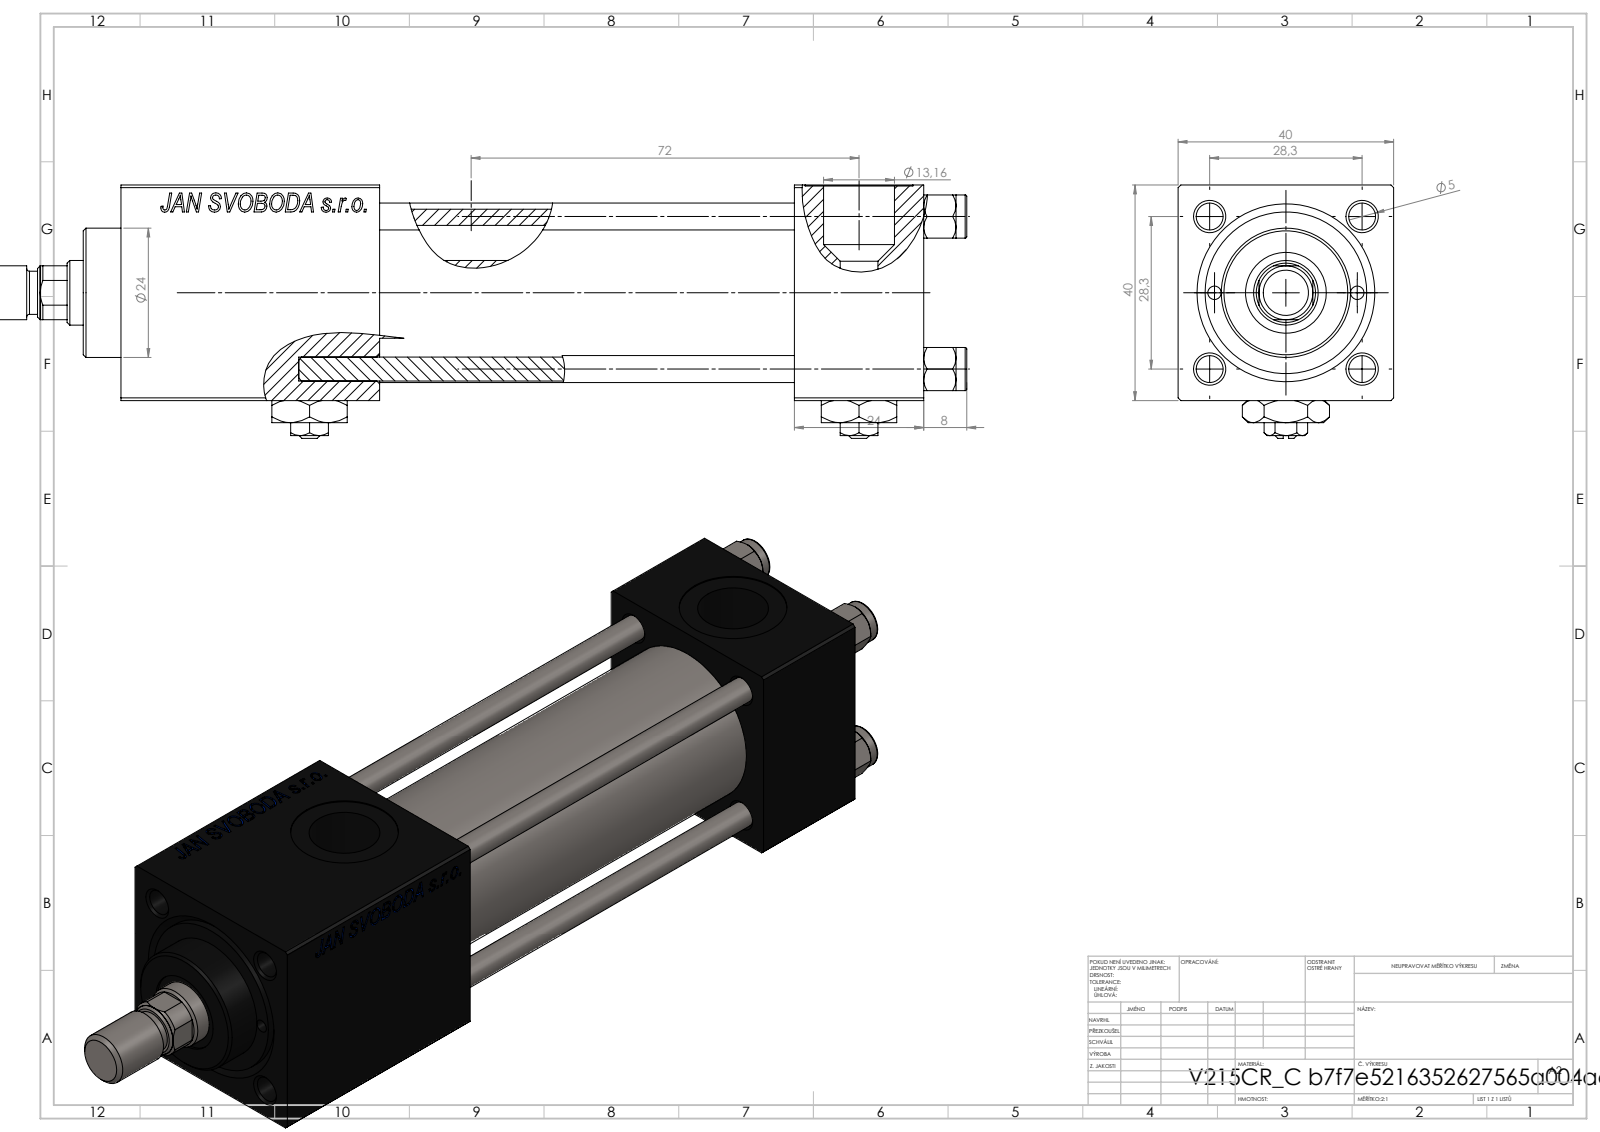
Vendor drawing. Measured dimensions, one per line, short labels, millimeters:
name: Zatka_pro_OIL_PORT; V215CR_C_TYCINKA; V215CR_C_Body; V215CR_VCP_C (+3 more)
written by: SolidWorks 2019 (CONFIG_CONTROL_DESIGN)
unit: mm
bodies: 13 solids, 313 faces (109 planar, 50 cylindrical, 154 other)
size: 186 × 45.15 × 37.54
volume: 58 019 mm³; area: 24 852 mm²
holes: 4× ⌀5, 2× ⌀2.5, 1× ⌀6.5, 1× ⌀12, 1× ⌀15
bosses: 5× ⌀8, 1× ⌀30, 1× ⌀25, 1× ⌀24, 1× ⌀10
rounds: 1× R5.5
face distances: 8, 96.3, 27, 69.3, 7, 4.3, 125, 98, 28.7, 51
hole spacings: 14.18, 20.01, 28.3, 30.84, 13.25, 40.02, 26.5
